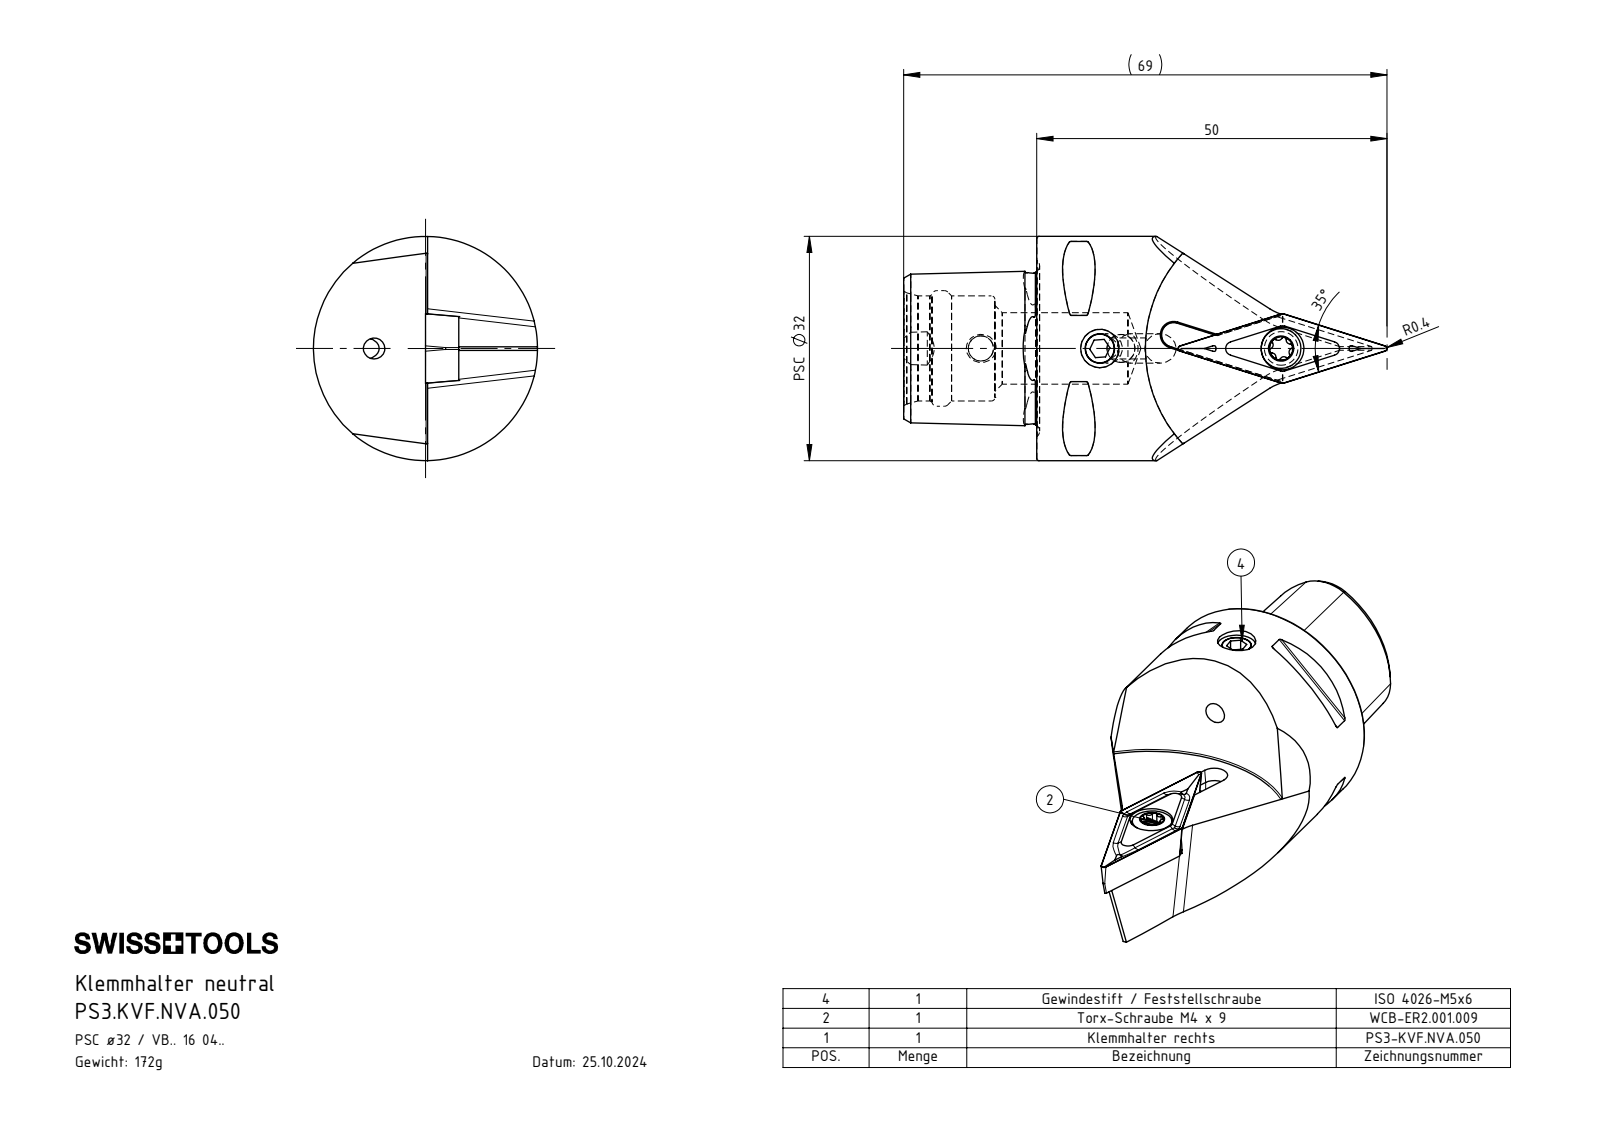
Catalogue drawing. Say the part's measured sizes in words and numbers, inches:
The part is named "PS3-KVF.NVA.050_A_mit kühlmitteldüse; ISO 4026 - M5 x 6_PreviewCfg; PS3.KVF.NVA.050; WCB-ER2.001.009_B (+1 more)". Its 3-D file was written by "SolidWorks 2022 (AUTOMOTIVE_DESIGN)". It is 4 solids with 267 faces: 65 planar, 68 cylindrical and 134 other. Overall it measures 2.717 by 1.26 by 1.26 inches. Its volume is 1.319 cubic inches and its surface area 13.43 square inches. Round holes: 1 of diameter 0.118, 1 of diameter 0.13, 1 of diameter 0.142, 1 of diameter 0.157, 1 of diameter 0.165, 1 of diameter 0.173, 1 of diameter 0.217, 1 of diameter 0.24, 1 of diameter 0.402, 1 of diameter 0.591, 1 of diameter 0.65. Round bosses or shafts: 1 of diameter 1.26, 1 of diameter 0.223, 1 of diameter 0.197, 1 of diameter 0.157, 1 of diameter 0.15. Partial cylindrical surfaces (rounded edges, fillets, slot ends): 8 of radius 0.012, 6 of radius 0.013, 6 of radius 0.023, 2 of radius 0.006, 2 of radius 0.276, 1 of radius 0.069, 1 of radius 0.157, 1 of radius 0.787. The main face-to-face distances are 0.176, 0.748, 0.473, 1.114, 0.236, 0.187, 0.512, 0.138, 0.74, 0.228. The hole center spacings are 0.787, 0.901, 0.909, 1.688, 1.696.
